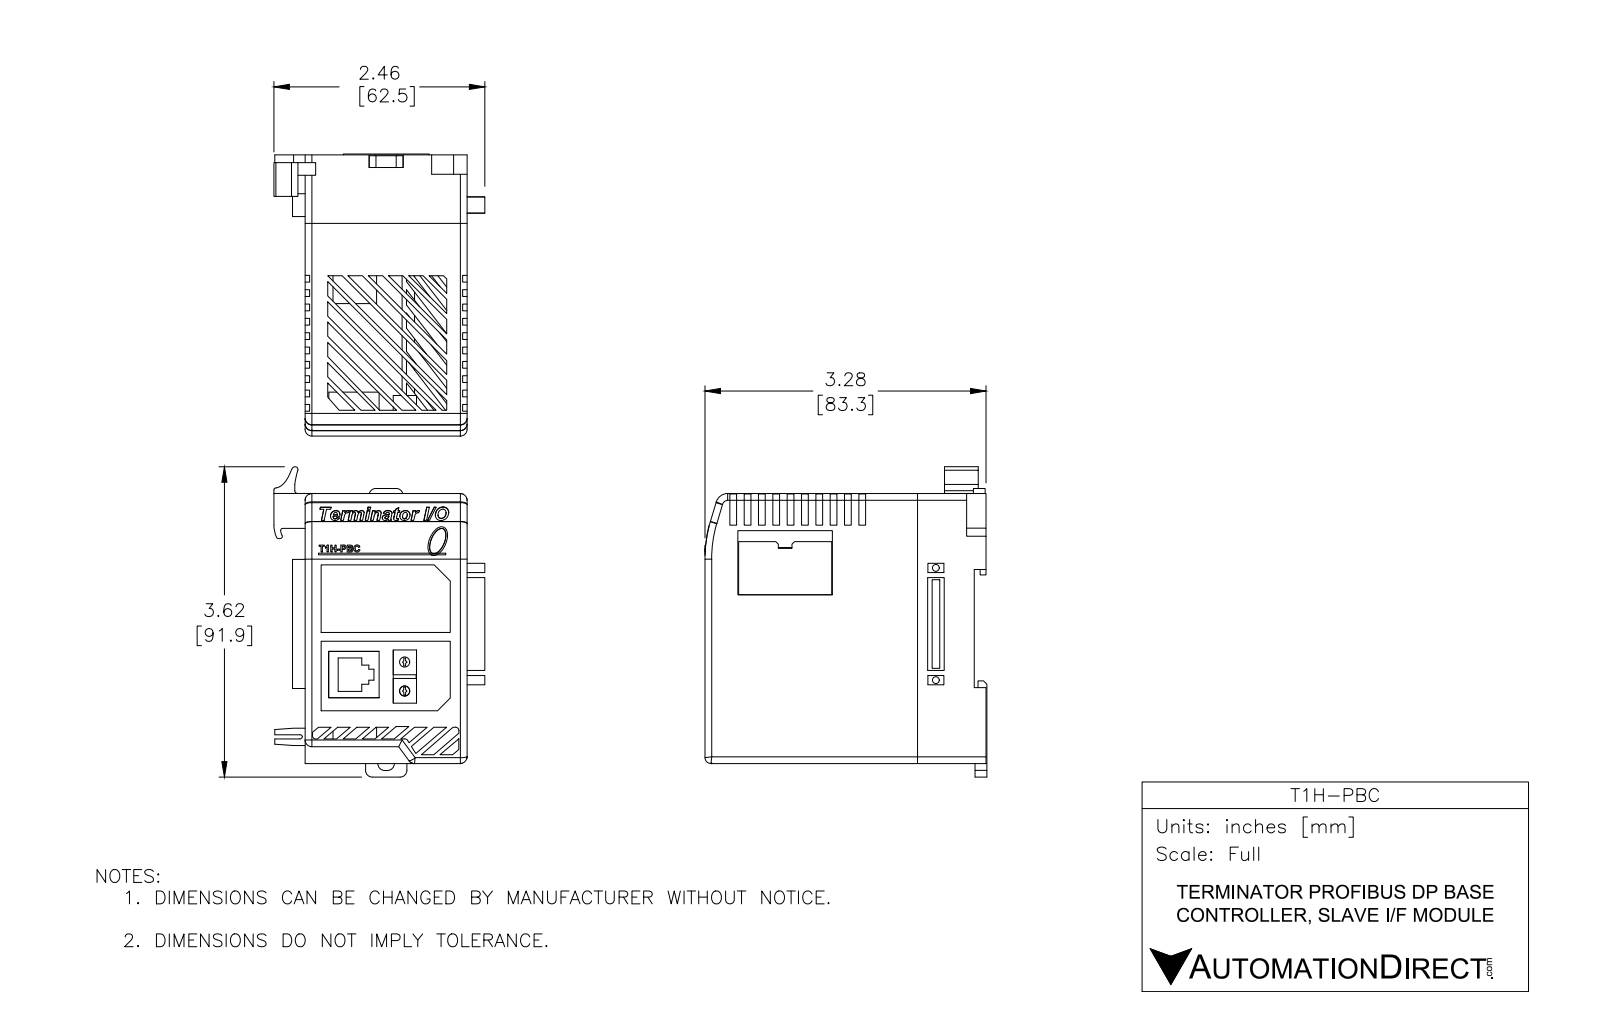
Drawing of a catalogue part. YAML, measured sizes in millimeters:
part_name: "T1H-PBC"
step_written_by: "SolidWorks 2013 (AUTOMOTIVE_DESIGN)"
units: millimeters
bodies: {solids: 22, faces: 973, planar: 732, cylindrical: 72, other: 169}
overall_size: [91.94, 83.59, 62.5]
volume: 106196
surface_area: 59196
round_holes:
  - {diameter: 2, count: 2}
  - {diameter: 3.01, count: 2}
round_bosses_or_shafts:
  - {diameter: 1.5, count: 2}
  - {diameter: 3.01, count: 1}
partial_cylinders:
  - {radius: 2, count: 18}
  - {radius: 1, count: 12}
  - {radius: 0.75, count: 4}
  - {radius: 2.06, count: 2}
  - {radius: 0.83, count: 1}
  - {radius: 0.94, count: 1}
  - {radius: 2.02, count: 1}
  - {radius: 2.04, count: 1}
face_to_face_distances: [2, 46, 48, 44, 1, 61, 3.5, 16.8, 77.8, 78]
hole_center_spacings: [8.58, 33.25]
